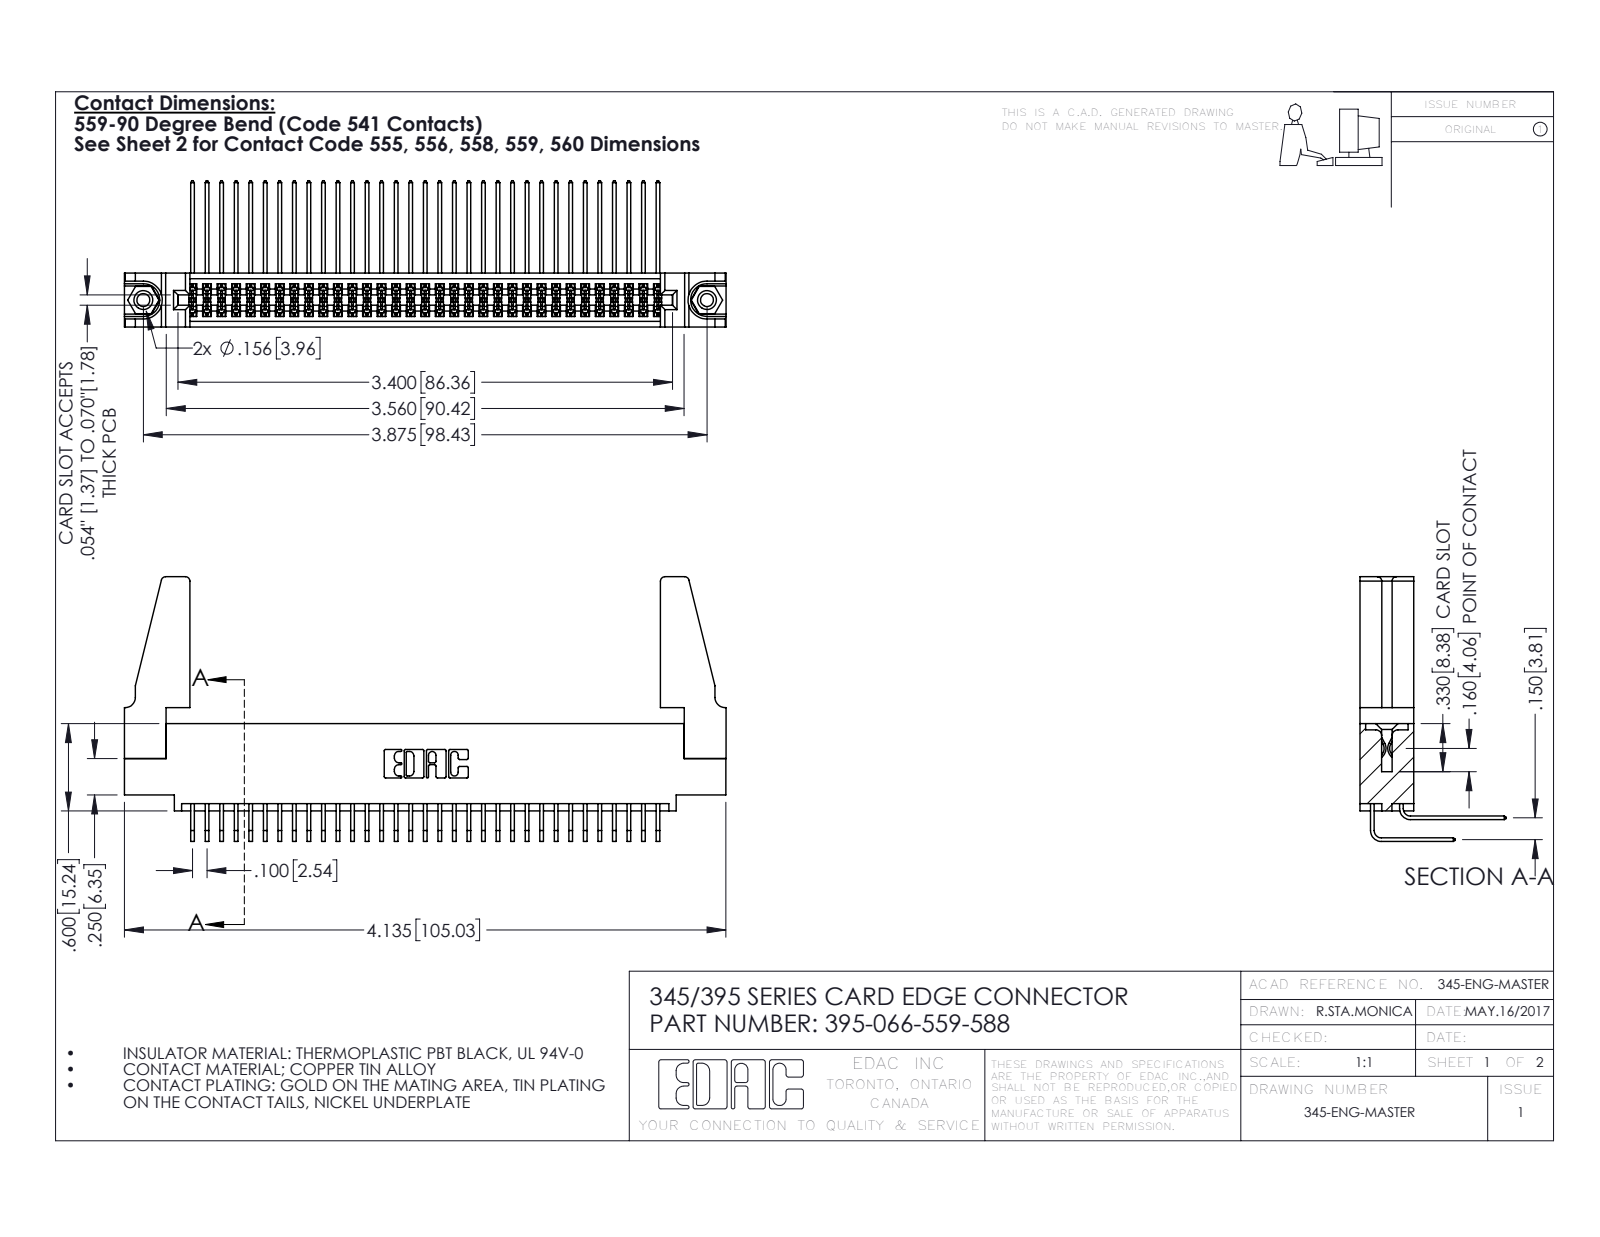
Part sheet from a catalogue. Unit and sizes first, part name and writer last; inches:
Units: inches
Overall size (bounding box): 4.136 × 1.819 × 1.005
Round holes (diameter × count): ⌀0.089 ×2, ⌀0.125 ×2, ⌀0.156 ×2, ⌀0.064 ×1
Round bosses / shafts (diameter × count): ⌀0.155 ×2
Partial cylindrical surfaces — rounded edges, fillets, slot ends (radius × count): R0.006 ×99, R0.01 ×22, R0.03 ×8, R0.007 ×6, R0.031 ×6, R0.026 ×3, R0.014 ×2, R0.019 ×2
Main face-to-face distances: 0.072, 0.298, 0.37, 0.2, 0.098, 0.272, 0.025, 0.225, 0.175, 0.15
Hole centre spacings: 0.27, 3.64, 3.875
Volume: 0.835 in³ · Surface area: 31.38 in²
Bodies: 71 solids, 3686 faces (2466 planar, 1204 cylindrical, 16 other)
Part name (STEP PRODUCT): 345 Part_0.110 Offset - 0.156 Dia-TH; 345-292-001_559 Tail - 2; 345-292-001_558 559 Tail - 1; 345-220-078_345-220-088 (+2 more)
STEP written by: SolidWorks 2016 (CONFIG_CONTROL_DESIGN)
